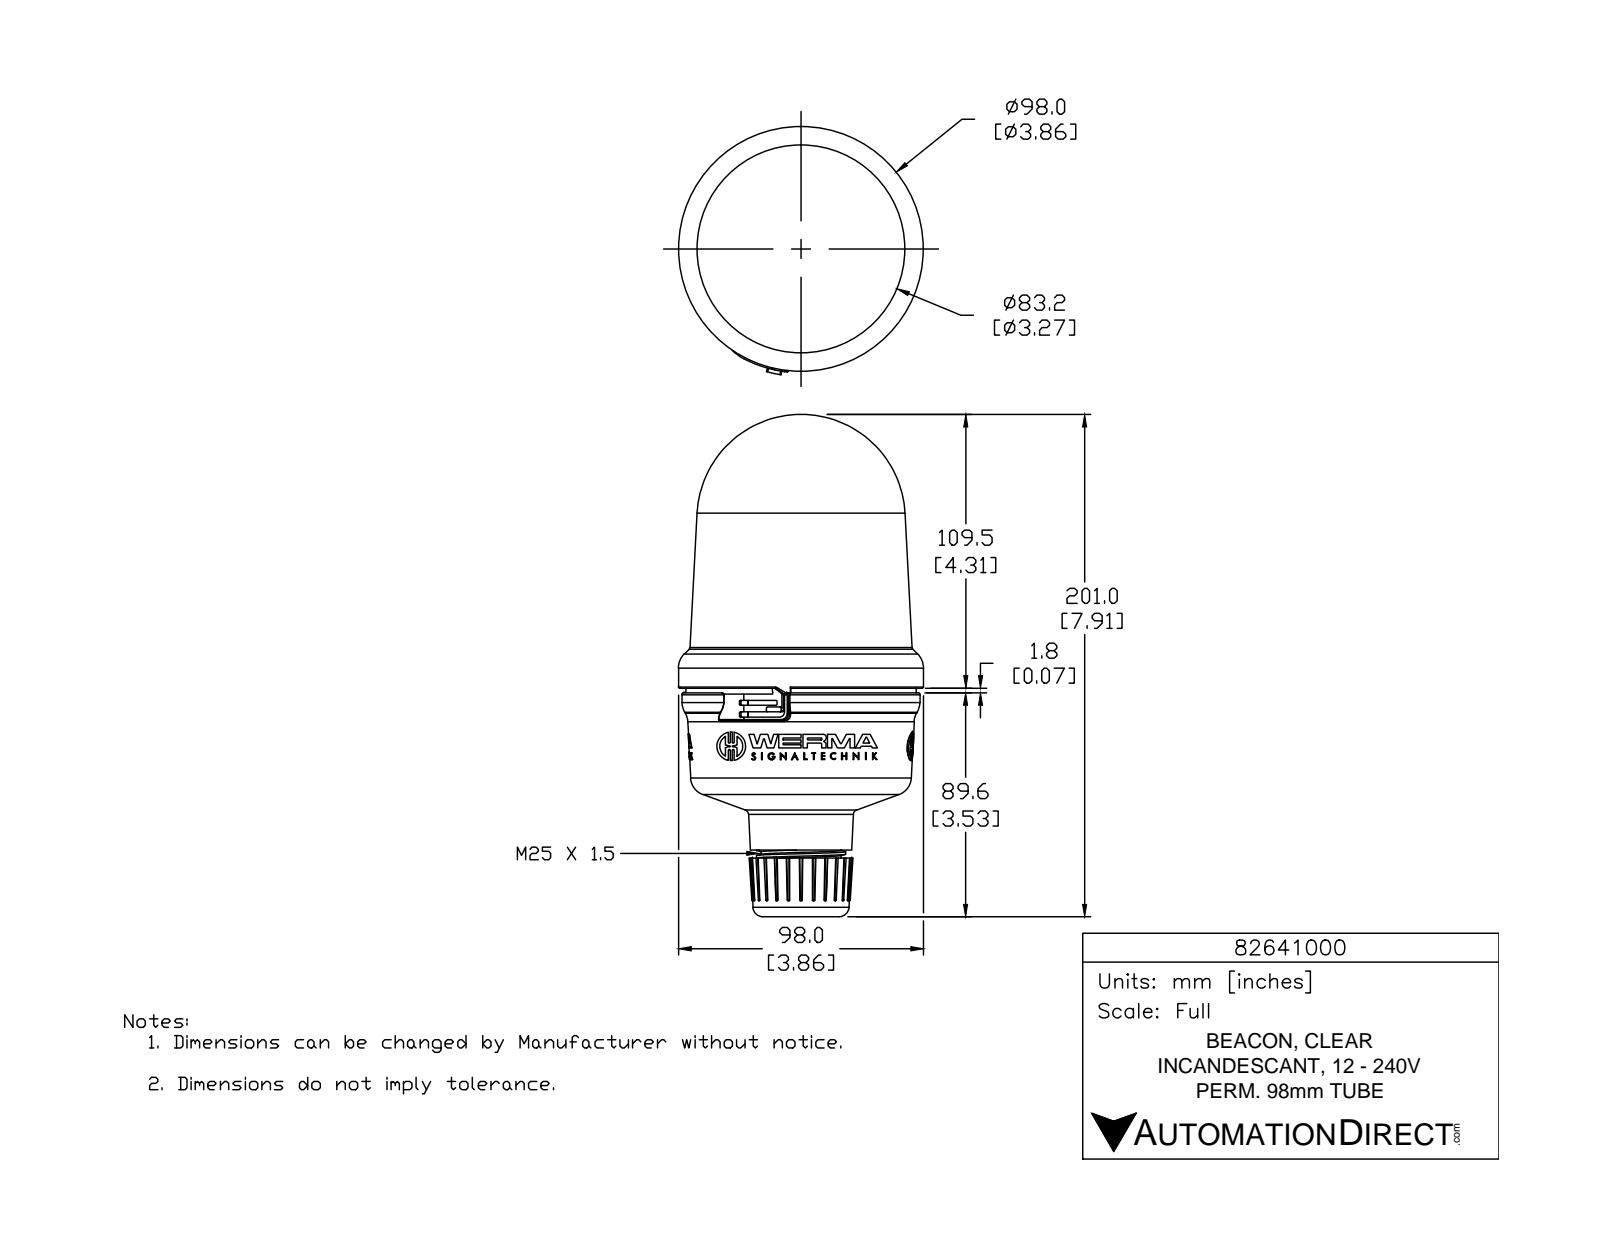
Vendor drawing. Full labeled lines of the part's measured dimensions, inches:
Part name (STEP PRODUCT): 82641000
STEP written by: SolidWorks 2015 (AUTOMOTIVE_DESIGN)
Units: inches
Bodies: 1 solid, 1006 faces (554 planar, 189 cylindrical, 263 other)
Overall size (bounding box): 7.914 × 3.912 × 3.858
Volume: 54.7 in³ · Surface area: 91.39 in²
Round holes (diameter × count): ⌀0.078 ×3, ⌀1.013 ×1, ⌀1.024 ×1
Round bosses / shafts (diameter × count): ⌀0.452 ×3, ⌀0.113 ×3, ⌀3.858 ×1, ⌀1.409 ×1, ⌀1.261 ×1
Partial cylindrical surfaces — rounded edges, fillets, slot ends (radius × count): R0.02 ×12, R0.007 ×9, R0.007 ×6, R0.016 ×6, R0.016 ×6, R0.016 ×6, R0.262 ×6, R0.006 ×3
Main face-to-face distances: 2.214, 0.462, 2.676, 0.335, 0.127, 2.548, 2.603, 2.476, 2.141, 0.073
